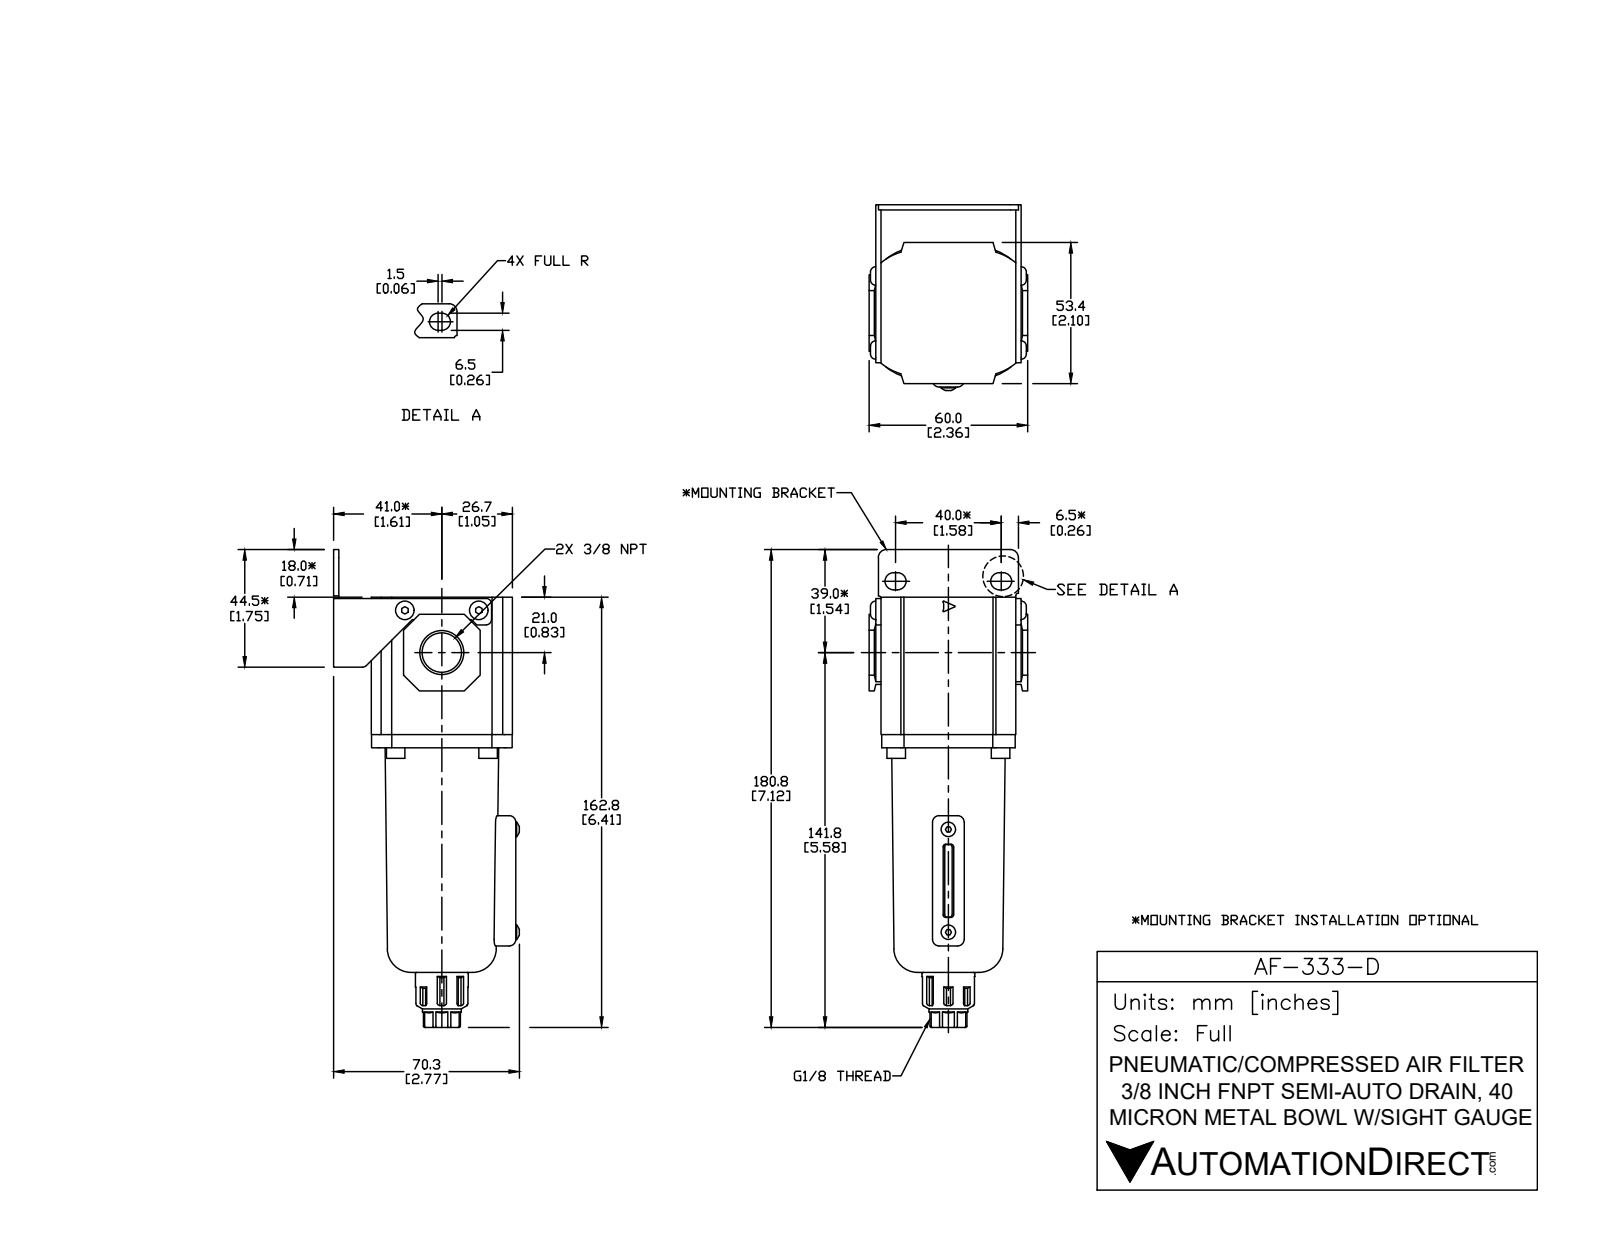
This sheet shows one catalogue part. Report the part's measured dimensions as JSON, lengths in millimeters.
{"part_name": "AF-333-D", "step_written_by": "SolidWorks 2015 (CONFIG_CONTROL_DESIGN)", "units": "millimeters", "bodies": {"solids": 9, "faces": 416, "planar": 245, "cylindrical": 98, "other": 73}, "overall_size": [181.1, 71, 60], "volume_mm3": 275147, "surface_area_mm2": 49805, "round_holes": [[3.4, 2], [6.2, 1], [14.27, 1]], "round_bosses_or_shafts": [[7, 4], [5.5, 2], [20, 1], [14.7, 1]], "partial_cylinders_radius": [[1.3, 8], [2.5, 8], [9.5, 8], [0.5, 6], [2, 5], [0.3, 4], [1, 4], [3.25, 4]], "face_to_face_distances": [2, 52, 51, 53, 53.4, 12.3, 14.3, 67.7, 65.7, 2.5], "hole_center_spacings": [21.06, 21.46, 28]}
